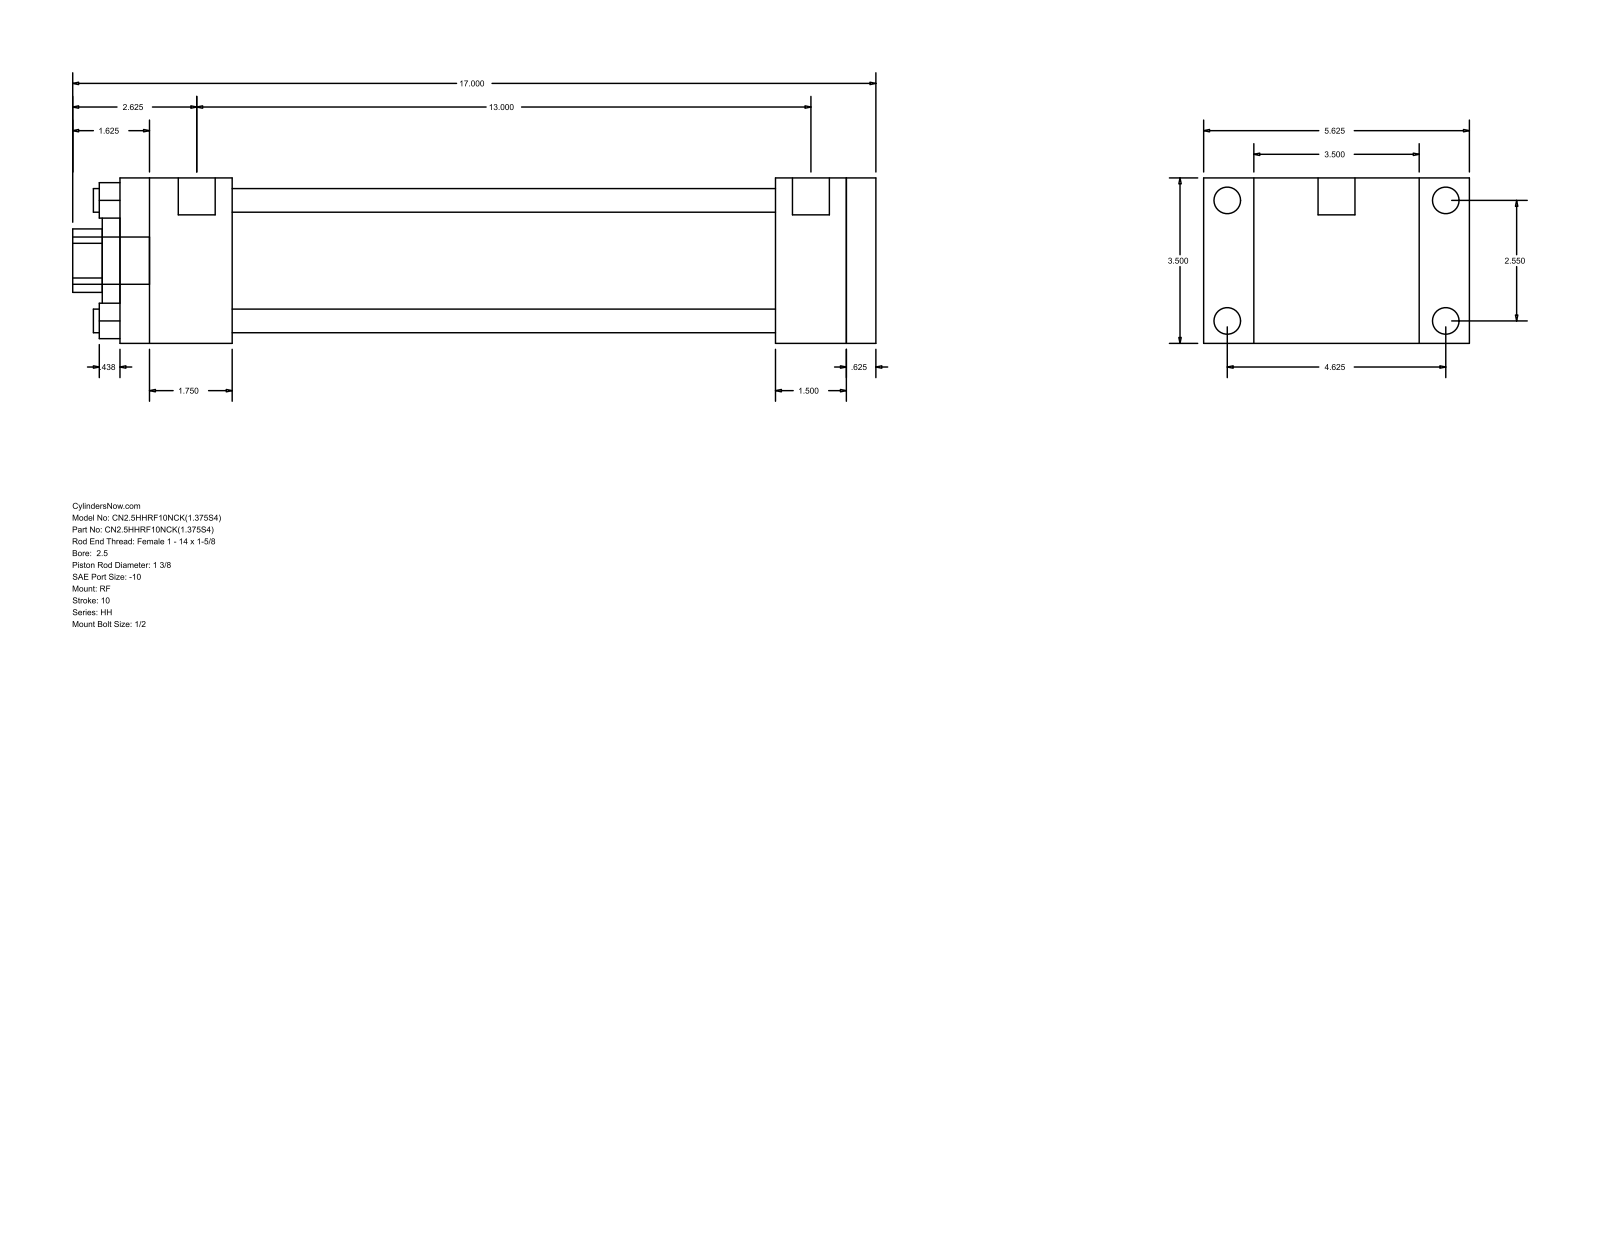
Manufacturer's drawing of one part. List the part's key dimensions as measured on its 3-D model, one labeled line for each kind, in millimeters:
Part name (STEP PRODUCT): HH_RF__0250_1.375
STEP written by: GSSL Pune (CONFIG_CONTROL_DESIGN)
Units: millimetres
Bodies: 0 solids, 92 faces (64 planar, 28 cylindrical, 0 other)
Overall size (bounding box): 431.8 × 142.88 × 88.9
Round holes (diameter × count): ⌀12.7 ×4, ⌀34.92 ×1, ⌀50.8 ×1, ⌀73.03 ×1
Round bosses / shafts (diameter × count): ⌀14.3 ×4, ⌀5.56 ×4, ⌀19.84 ×2, ⌀25.4 ×1
Partial cylindrical surfaces — rounded edges, fillets, slot ends (radius × count): R17.06 ×1
Main face-to-face distances: 88.9, 15.87, 390.53, 406.4, 60.32, 330.21, 346.08, 352.42, 292.1, 38.11
Hole centre spacings: 45.79, 64.76, 91.58
